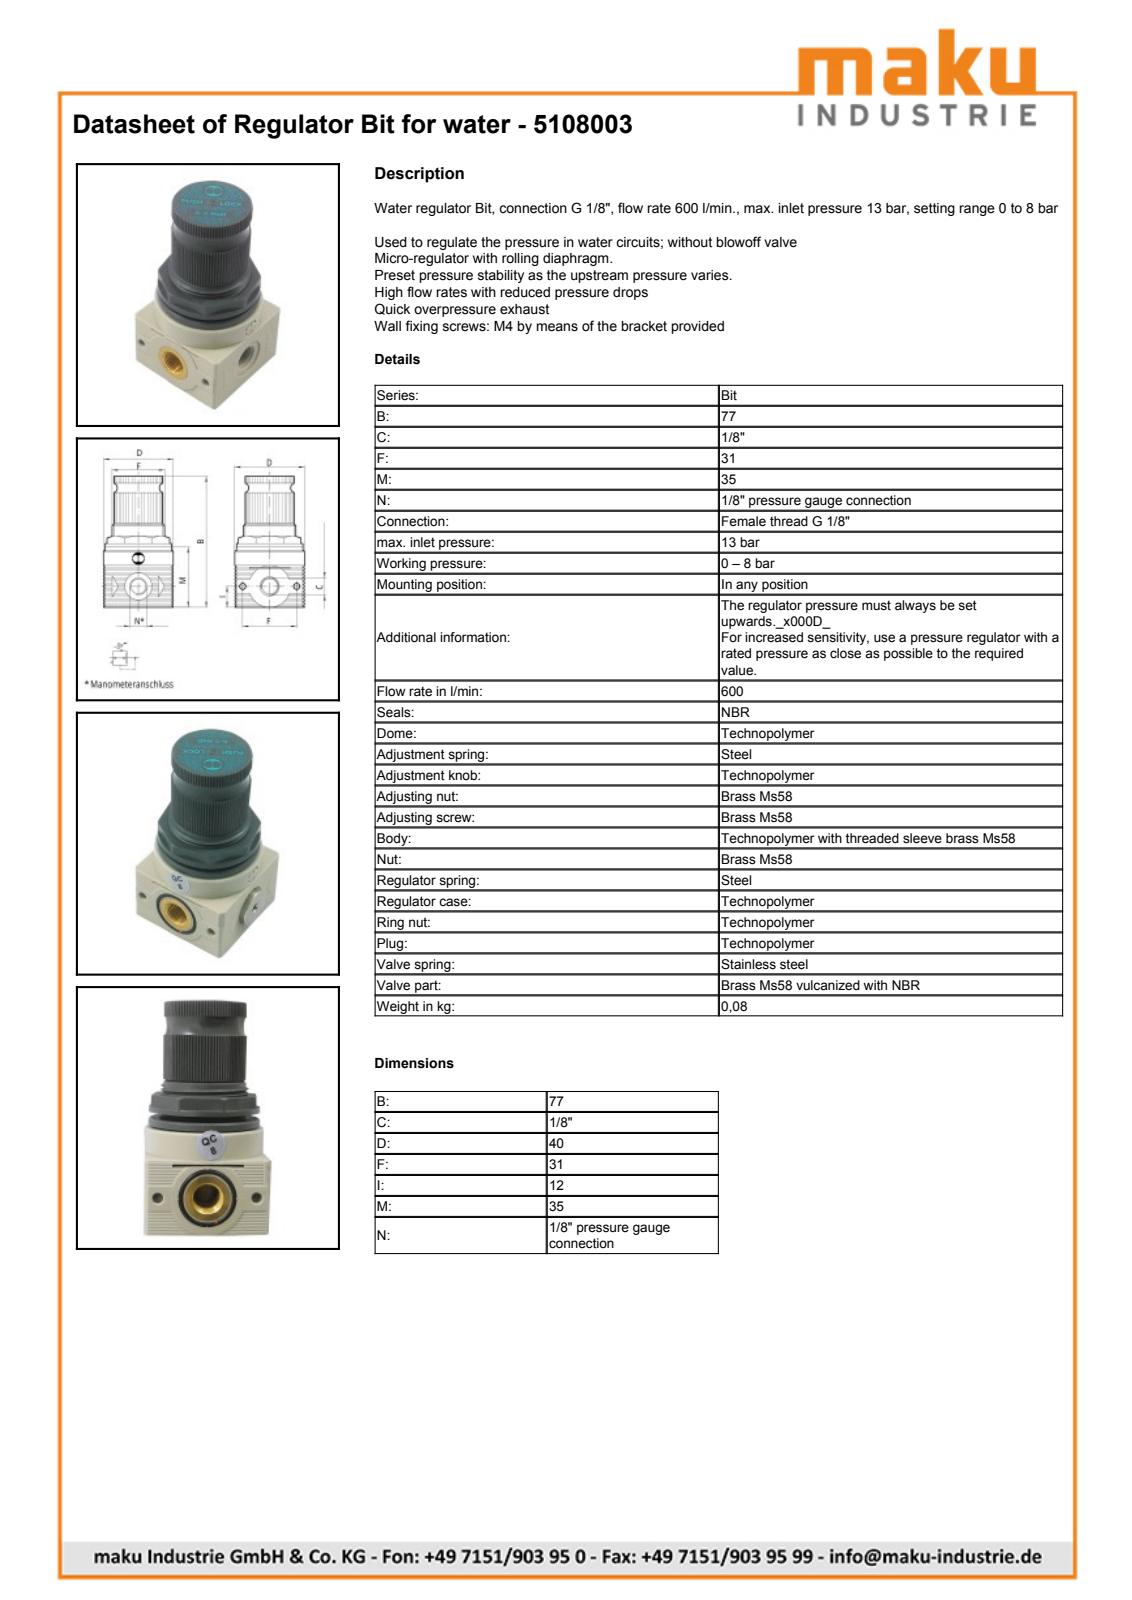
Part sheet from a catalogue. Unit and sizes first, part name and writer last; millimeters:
Units: millimetres
Overall size (bounding box): 77 × 41.5 × 40
Round holes (diameter × count): ⌀4 ×2, ⌀8.57 ×2, ⌀15.5 ×1
Round bosses / shafts (diameter × count): ⌀39.9 ×1, ⌀38 ×1, ⌀37.6 ×1, ⌀30 ×1, ⌀28 ×1, ⌀24 ×1, ⌀15 ×1, ⌀9.73 ×1
Partial cylindrical surfaces — rounded edges, fillets, slot ends (radius × count): R12 ×1
Main face-to-face distances: 32, 40, 1, 9, 10, 39.95, 77, 45, 39, 19
Hole centre spacings: 15.5, 31
Volume: 77 227 mm³ · Surface area: 18 175 mm²
Bodies: 3 solids, 127 faces (92 planar, 27 cylindrical, 8 other)
Part name (STEP PRODUCT): 5108003; 5108003-BD; 5108003-KN; 1/8-BIT
STEP written by: PARTsolutions (AUTOMOTIVE_DESIGN)
